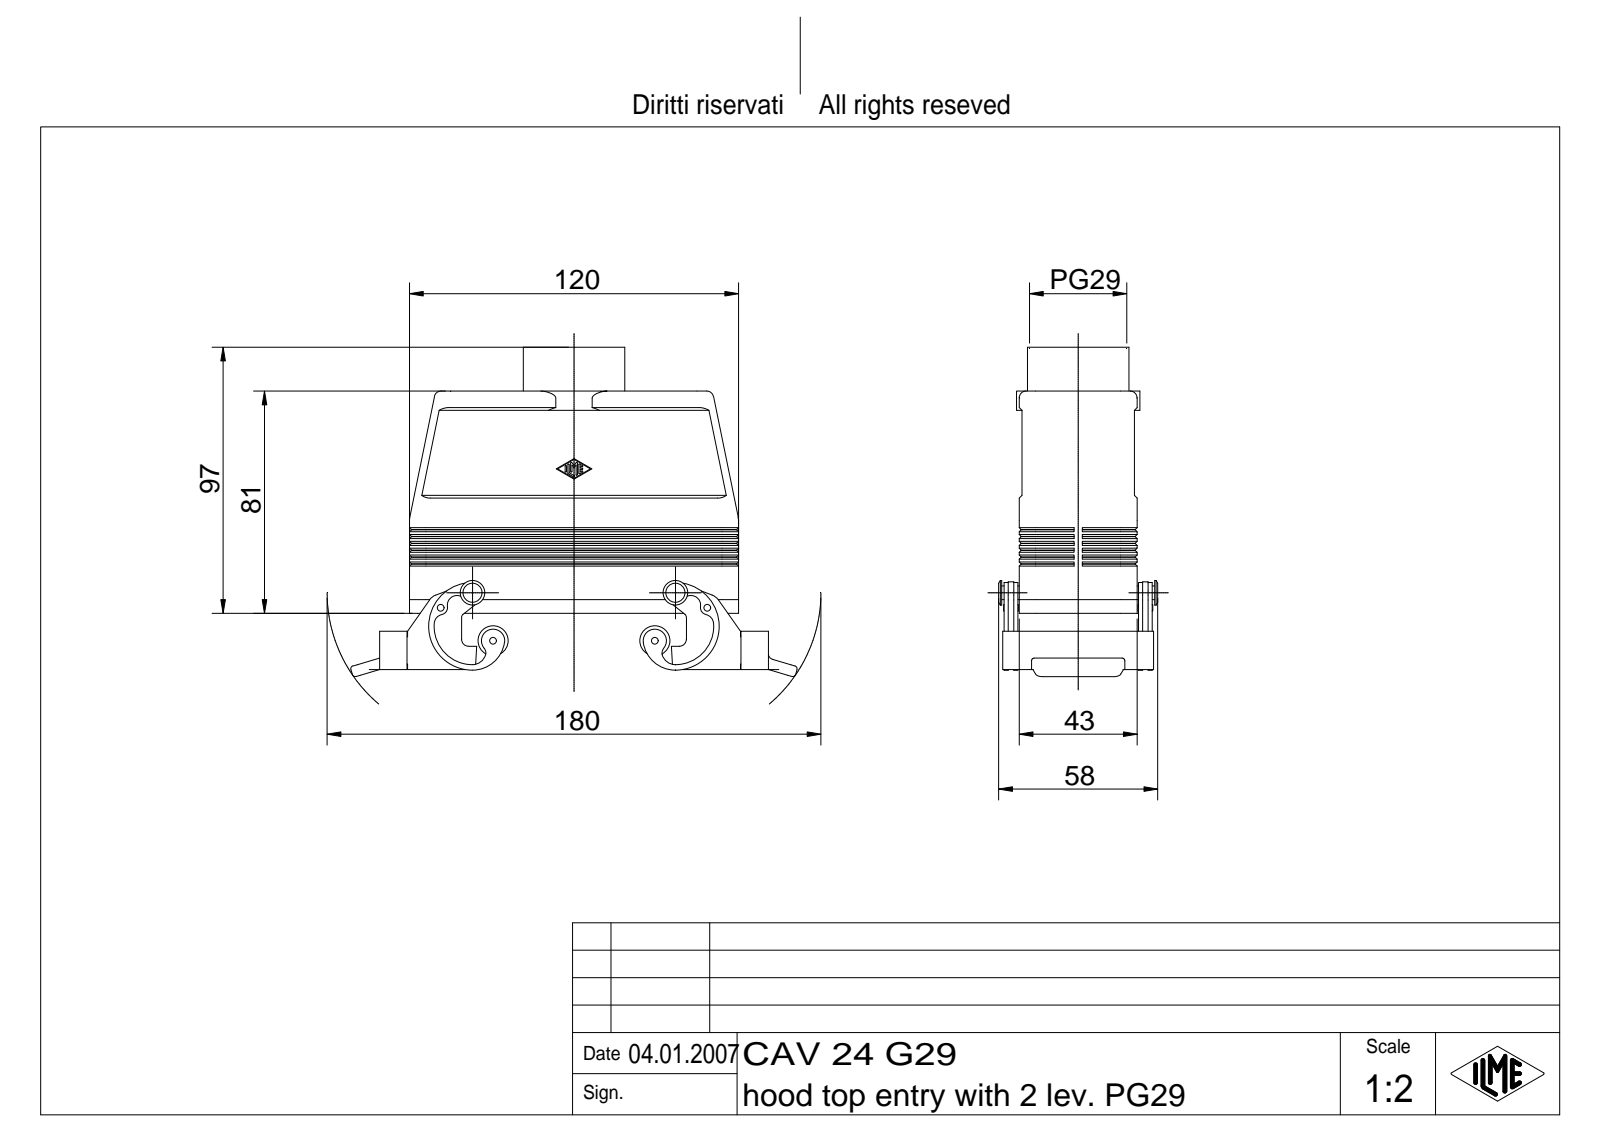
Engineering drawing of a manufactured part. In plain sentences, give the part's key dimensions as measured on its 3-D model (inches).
The part is named "CAV Tüllengehäuse 2 Bügel für einen Einsatz". Its 3-D file was written by "Autodesk Inventor 7 (AUTOMOTIVE_DESIGN)". It is 1 solid with 965 faces: 302 planar, 256 cylindrical and 407 other. Overall it measures 6.409 by 4.728 by 2.283 inches. Its volume is 7.731 cubic inches and its surface area 117.3 square inches. Round holes: 2 of diameter 0.098, 1 of diameter 1.318, 1 of diameter 1.397. Round bosses or shafts: 2 of diameter 0.433, 2 of diameter 0.354, 2 of diameter 0.197, 2 of diameter 0.079, 1 of diameter 1.772, 1 of diameter 1.457. Partial cylindrical surfaces (rounded edges, fillets, slot ends): 14 of radius 0.01, 12 of radius 0.039, 10 of radius 0.098, 10 of radius 0.236, 8 of radius 0.118, 7 of radius 0.079, 4 of radius 0.138, 4 of radius 0.197. The main face-to-face distances are 0.157, 0.118, 1.535, 1.378, 1.496, 0.039, 1.654, 1.693, 1.614, 0.276. The hole center spacings are 3.827.
